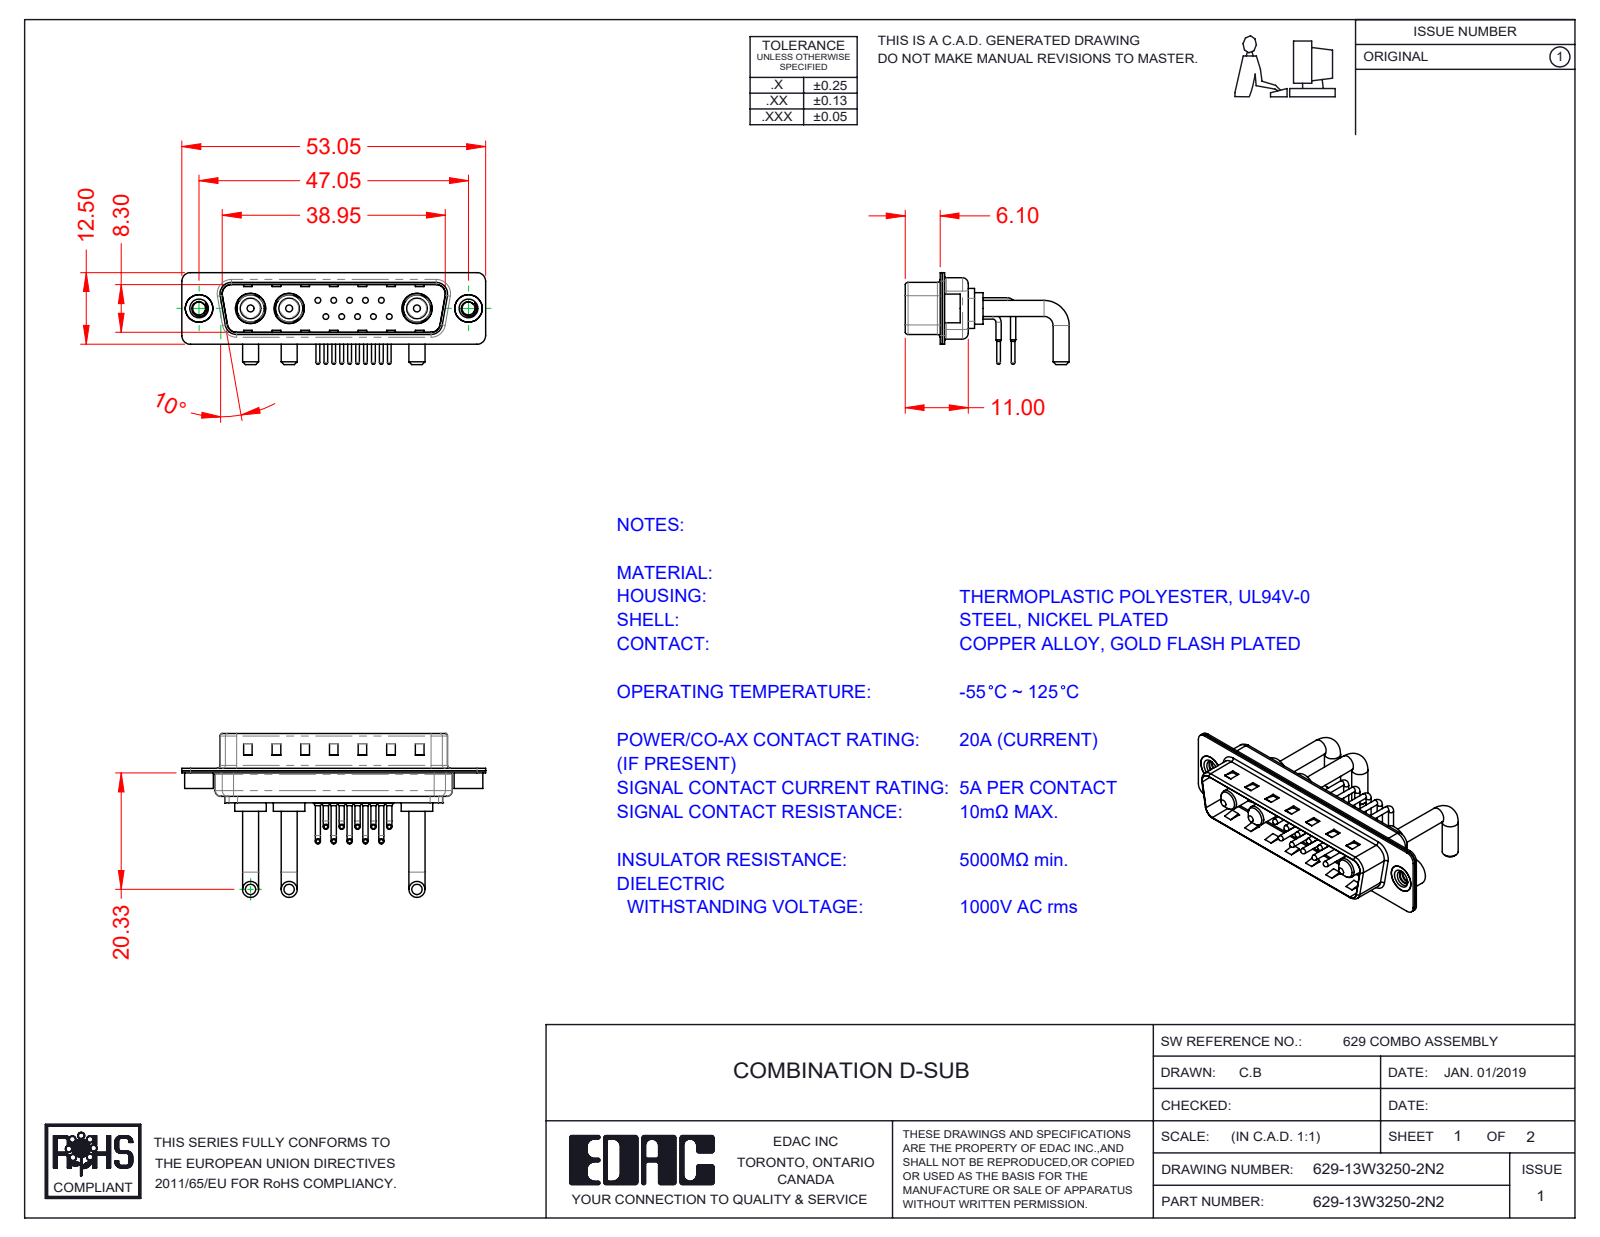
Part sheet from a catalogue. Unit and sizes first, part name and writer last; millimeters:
Units: millimetres
Overall size (bounding box): 53.05 × 28.63 × 16.05
Round holes (diameter × count): ⌀0.75 ×10, ⌀1.6 ×10, ⌀2 ×10, ⌀4.85 ×3, ⌀5.3 ×3, ⌀2.26 ×2, ⌀4 ×2, ⌀4.8 ×2
Round bosses / shafts (diameter × count): ⌀0.9 ×20, ⌀1.5 ×10, ⌀1 ×10, ⌀0.65 ×10, ⌀2.8 ×6, ⌀5.5 ×3, ⌀5.2 ×3, ⌀4.75 ×3
Partial cylindrical surfaces — rounded edges, fillets, slot ends (radius × count): R1.5 ×16, R2 ×12, R1.01 ×10, R0.5 ×8, R1.6 ×8, R0.25 ×4, R0.6 ×4, R0.65 ×4
Main face-to-face distances: 0.4, 0.8, 9.5, 9.1, 8.7, 9.9, 5.6, 0.75, 1.2, 0.35
Hole centre spacings: 3.16, 2.77, 5.04, 5.54, 7.49, 5.03, 8.31, 10.11
Volume: 3 342 mm³ · Surface area: 7 559 mm²
Bodies: 21 solids, 1605 faces (841 planar, 560 cylindrical, 204 other)
Part name (STEP PRODUCT): 629Combo Shell Rear_25 Contacts; 629Combo Contact Row 2; 629-13W3250-2N2; 629Combo Threaded Rivet_2 (+4 more)
STEP written by: SolidWorks 2020 (CONFIG_CONTROL_DESIGN)
